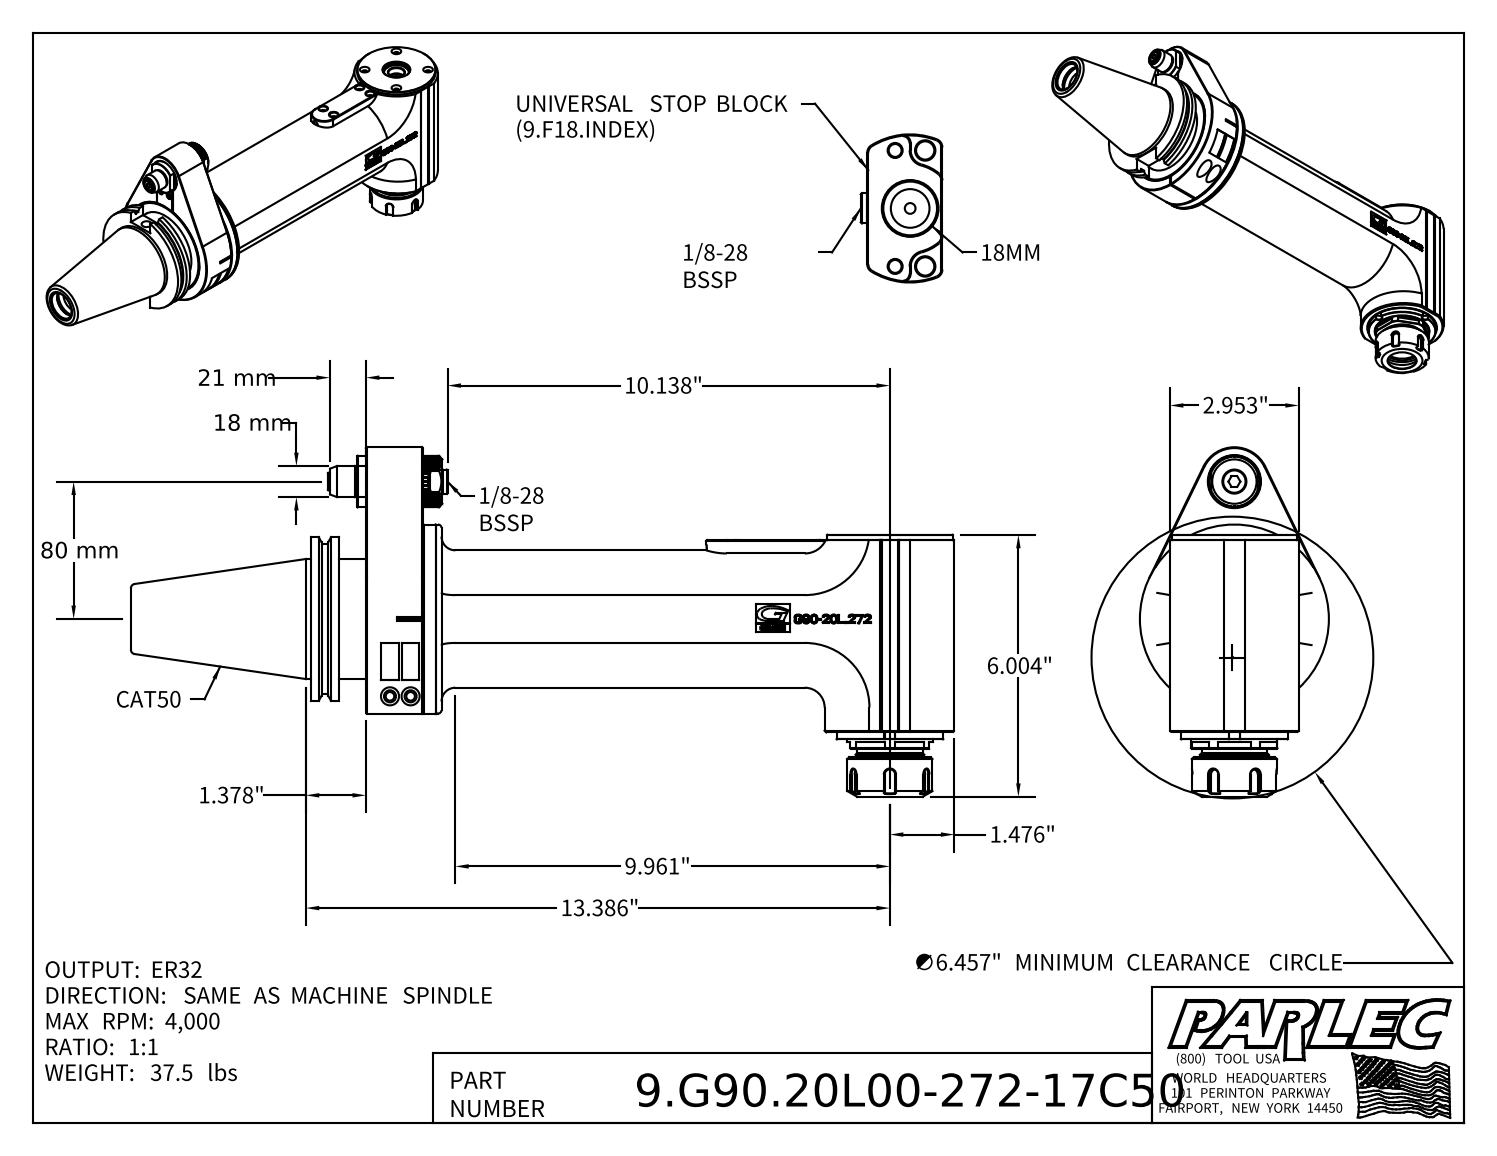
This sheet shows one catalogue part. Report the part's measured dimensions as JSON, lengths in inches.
{"part_name": "9.G90.20L00-272-17C50; 9_G90_20L00-272; 9_GA2_458_1 (Classic, Type 2, Cat50, 80mm)", "step_written_by": "Autodesk Inventor 2022 (AUTOMOTIVE_DESIGN)", "units": "inches", "bodies": {"solids": 20, "faces": 1443, "planar": 854, "cylindrical": 261, "other": 328}, "overall_size": [18.87, 8.012, 4.331], "volume_in3": 147.1, "surface_area_in2": 455.7, "round_holes": [[0.197, 12], [0.13, 9], [0.177, 8], [0.165, 4], [0.315, 4], [0.335, 3], [0.157, 2], [0.236, 2], [0.276, 2], [0.413, 2], [0.433, 2], [0.346, 1]], "round_bosses_or_shafts": [[0.394, 2], [4.331, 1], [4.016, 1], [3.875, 1], [3.593, 1], [3.524, 1], [3.15, 1], [2.874, 1]], "partial_cylinders_radius": [[0.118, 9], [0.098, 5], [0.085, 2], [0.224, 2], [0.315, 2], [0.469, 2], [0.472, 2], [1.575, 2]], "face_to_face_distances": [1.299, 2.953, 0.315, 0.984, 0.626, 0.197, 0.118, 0.941, 1.567, 1.925], "hole_center_spacings": [1.87, 0.968, 2.645, 3.239, 3.613, 3.74, 0.217, 0.35]}
